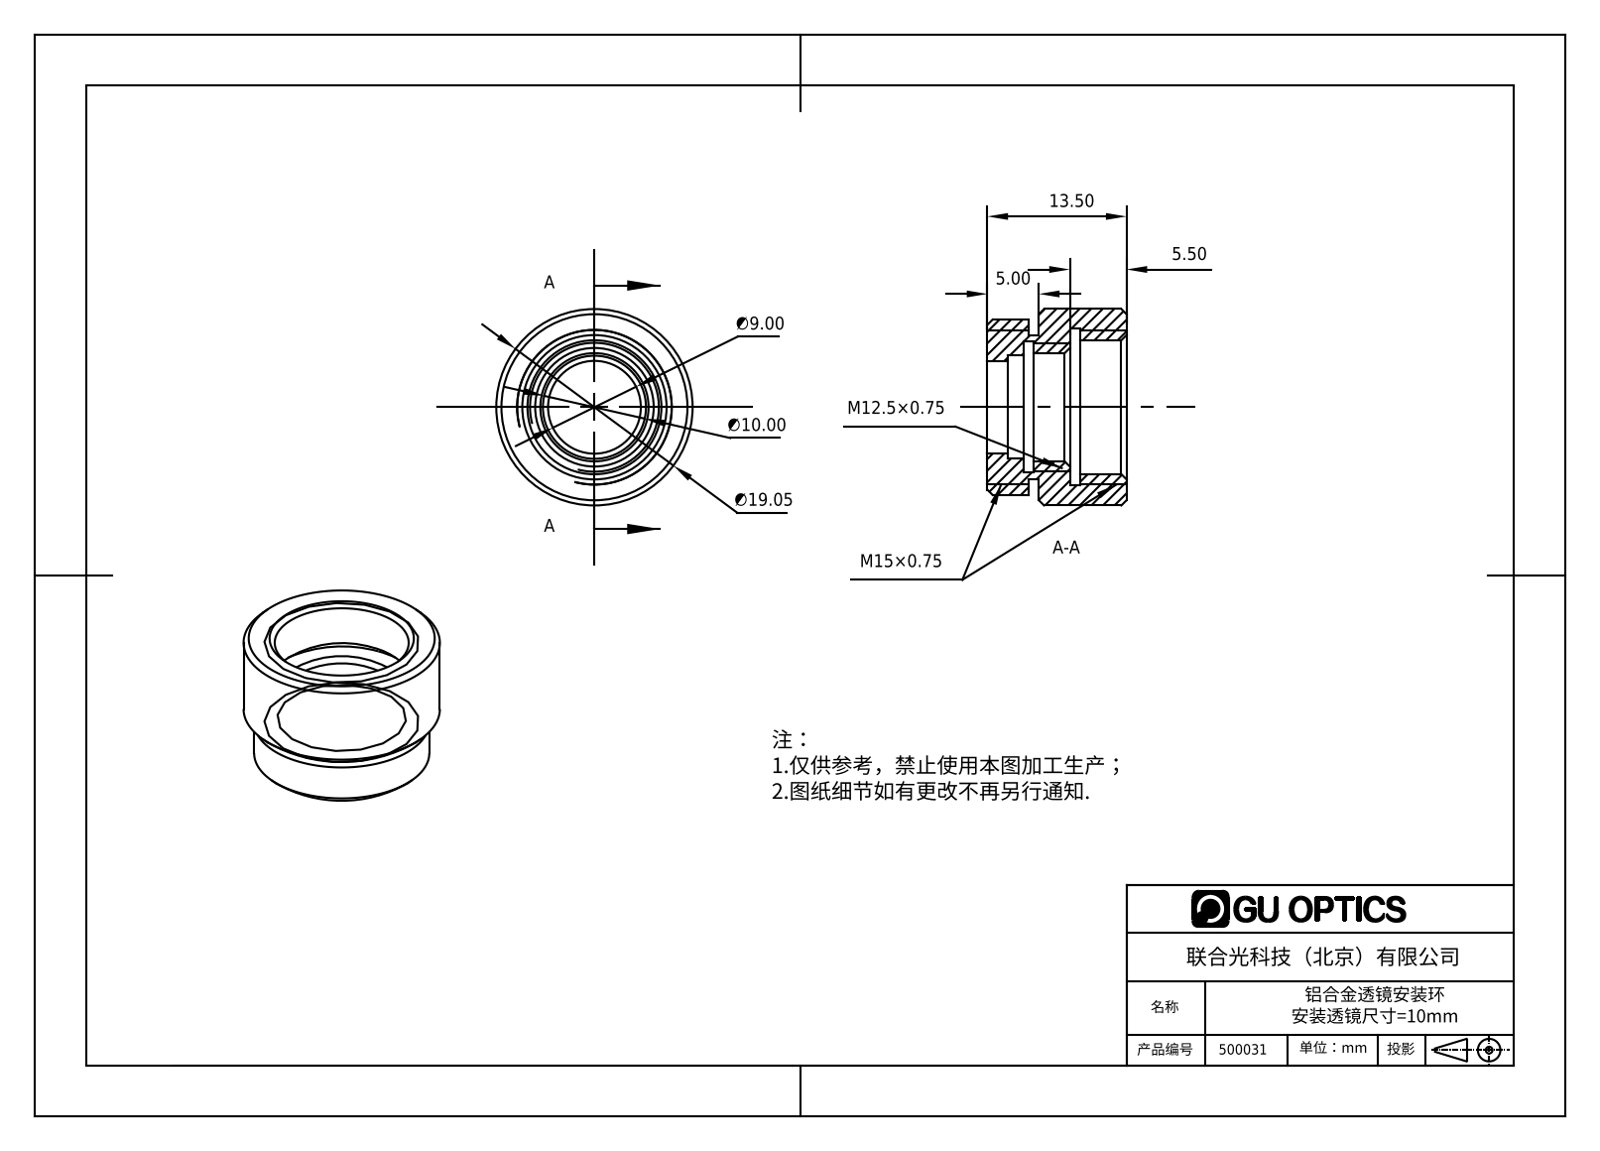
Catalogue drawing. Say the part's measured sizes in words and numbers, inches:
The part is named "500031". Its 3-D file was written by "SolidWorks 2016 (AUTOMOTIVE_DESIGN)". It is 1 solid with 37 faces: 9 planar, 18 cylindrical and 10 other. Overall it measures 0.75 by 0.75 by 0.531 inches. Its volume is 0.122 cubic inches and its surface area 3.024 square inches. Round holes: 1 of diameter 0.354, 1 of diameter 0.394, 1 of diameter 0.413, 1 of diameter 0.5, 1 of diameter 0.512, 1 of diameter 0.598. Round bosses or shafts: 1 of diameter 0.75, 1 of diameter 0.669, 1 of diameter 0.551. The main face-to-face distances are 0.157, 0.177, 0.039, 0.197, 0.02, 0.217, 0.531, 0.335, 0.118, 0.354.
